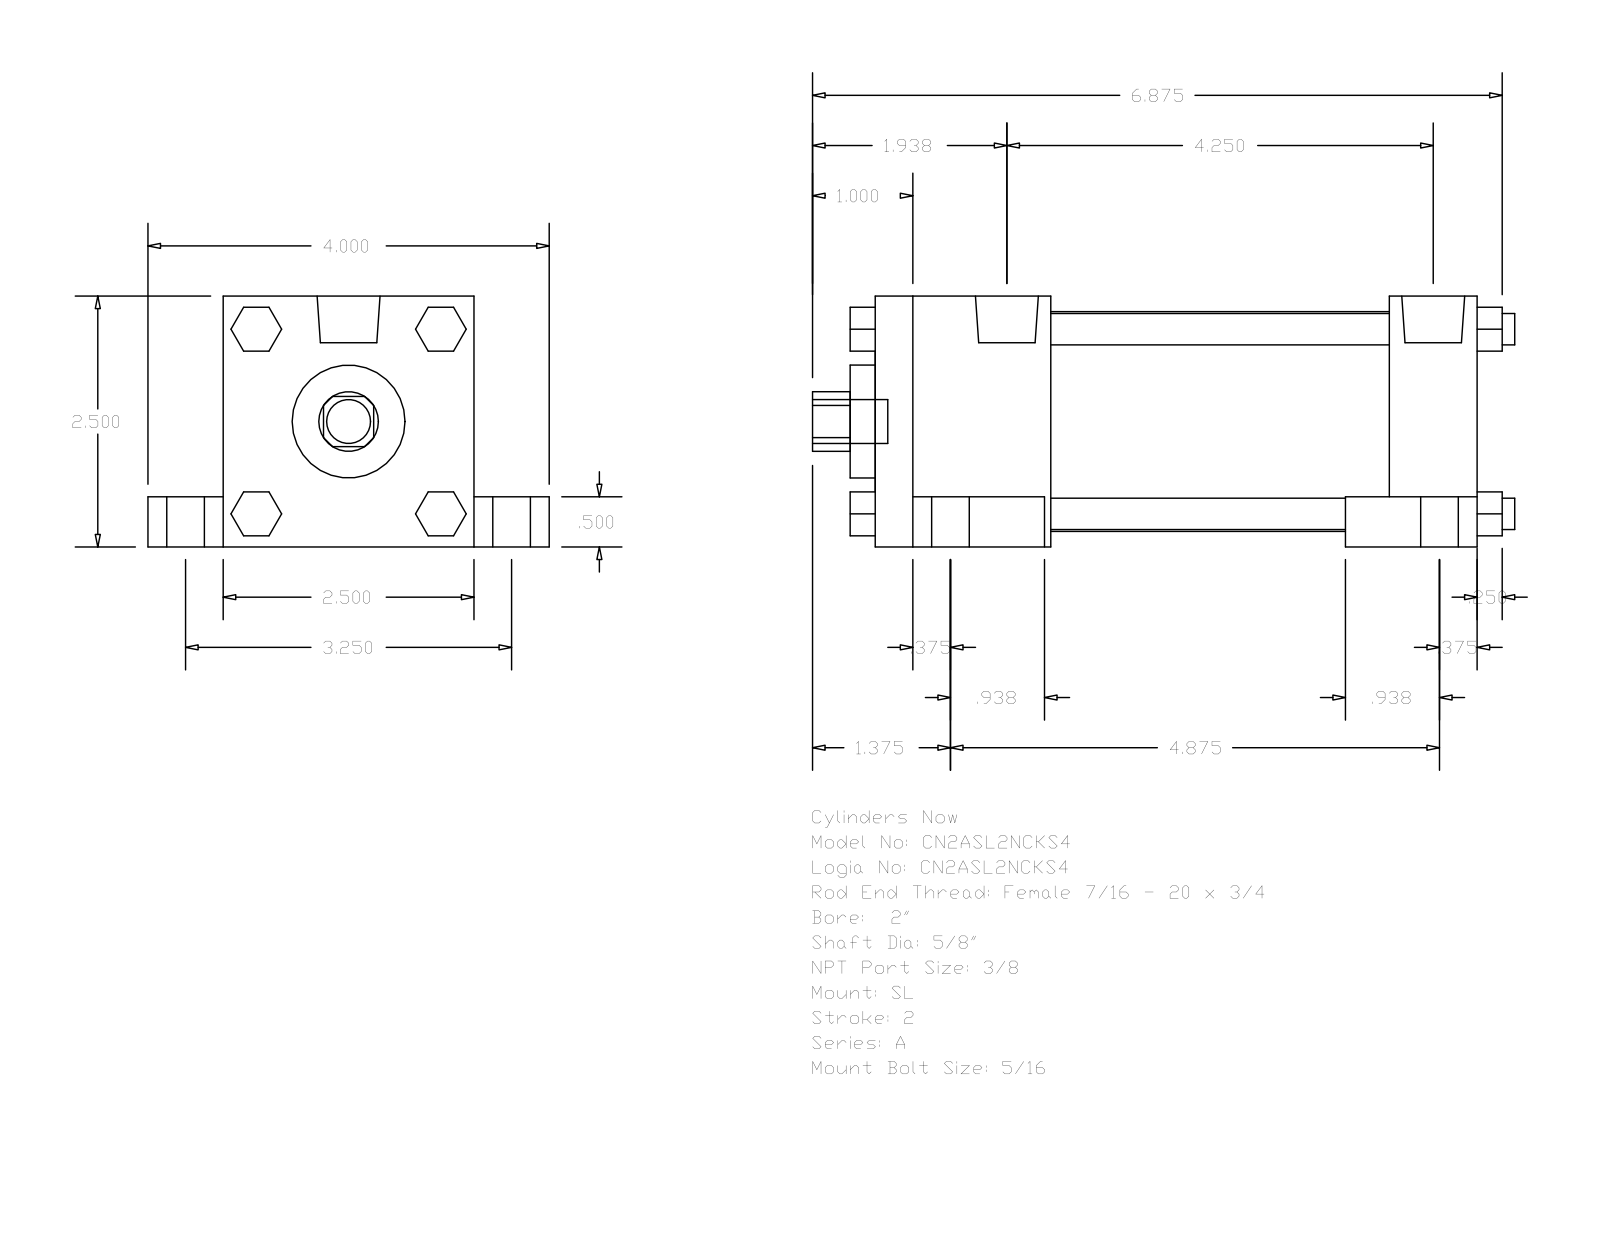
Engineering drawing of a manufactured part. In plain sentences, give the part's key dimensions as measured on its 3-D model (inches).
The part is named "A_SL__0200_0.625". Its 3-D file was written by "GSSL Pune (CONFIG_CONTROL_DESIGN)". It is 0 solids with 148 faces: 112 planar, 36 cylindrical and 0 other. Overall it measures 7 by 4 by 2.5 inches. Round holes: 1 of diameter 0.625, 1 of diameter 1.125, 1 of diameter 2.19. Round bosses or shafts: 4 of diameter 0.625, 4 of diameter 0.375, 4 of diameter 0.313, 4 of diameter 0.219, 2 of diameter 0.627, 1 of diameter 0.437. Partial cylindrical surfaces (rounded edges, fillets, slot ends): 1 of radius 0.297. The main face-to-face distances are 2.5, 6, 2, 0.5, 0.75, 3.25, 1.75, 4.25, 5.125, 3.375.
